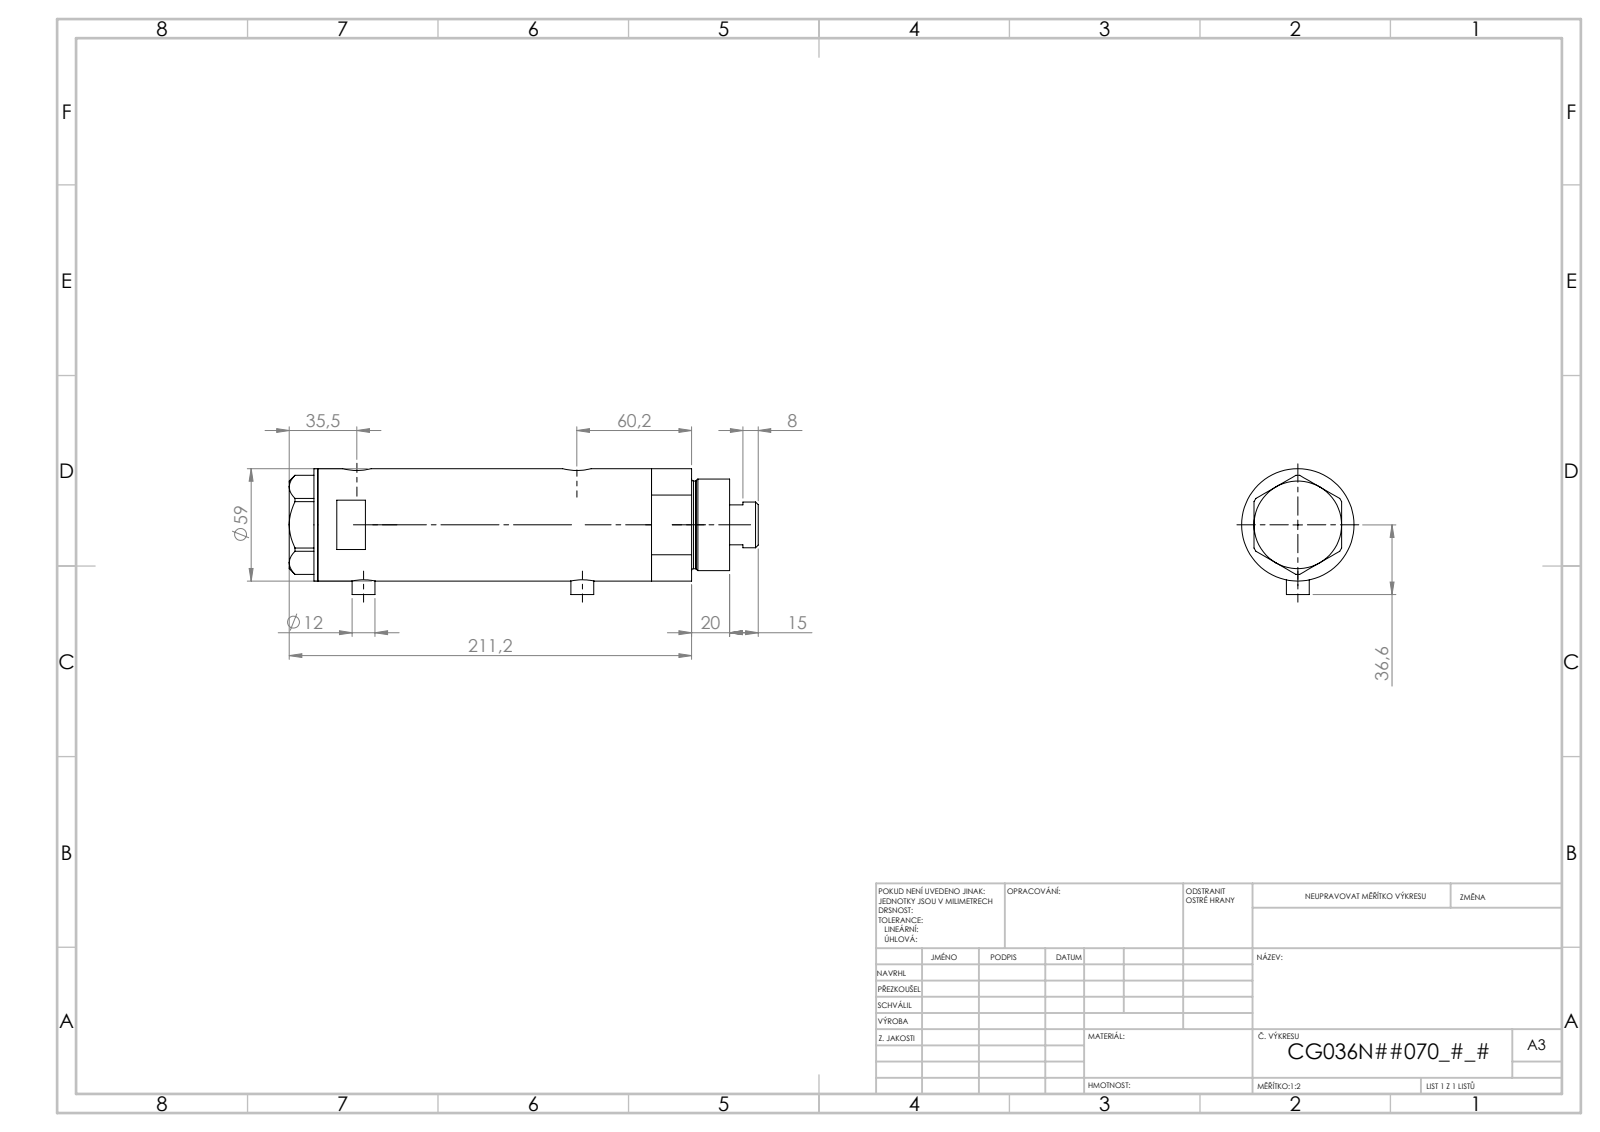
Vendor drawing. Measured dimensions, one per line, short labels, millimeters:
name: V270CG_FRONT; V270CG_BACK; V270CG_VC; V270CG_MIDDLE
written by: SolidWorks 2019 (CONFIG_CONTROL_DESIGN)
unit: mm
bodies: 4 solids, 126 faces (53 planar, 53 cylindrical, 20 other)
size: 233.42 × 60.1 × 59
volume: 525 629 mm³; area: 108 282 mm²
holes: 2× ⌀5, 2× ⌀9.73, 2× ⌀12.5, 2× ⌀15, 1× ⌀8.5, 1× ⌀25, 1× ⌀26.5, 1× ⌀36, 1× ⌀40, 1× ⌀52
bosses: 2× ⌀12, 1× ⌀59, 1× ⌀48, 1× ⌀46, 1× ⌀24
face distances: 127.34, 23.5, 103.84, 15, 38.5, 142.34, 218.42, 203.42, 179.92, 76.08
hole spacings: 2.9, 3.5, 102.15, 105.05, 105.65, 108.55, 2.89, 2.91
